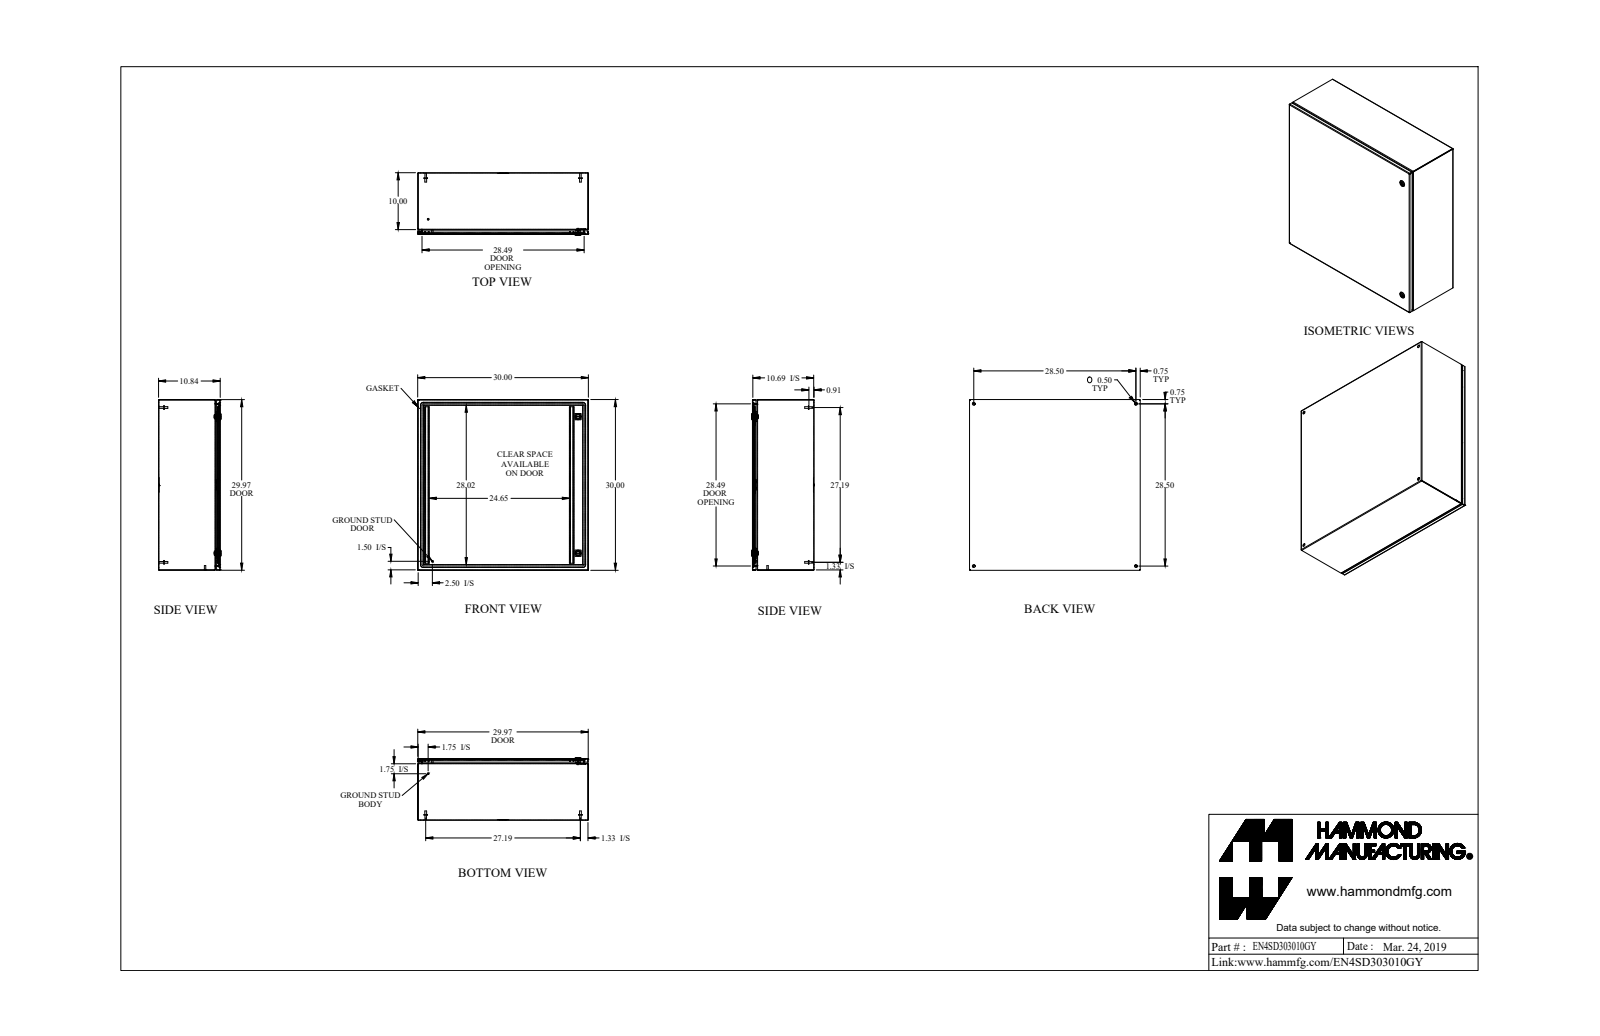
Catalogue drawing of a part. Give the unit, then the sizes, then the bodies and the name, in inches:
Units: inches
Overall size (bounding box): 30 × 30 × 10.997
Round holes (diameter × count): ⌀0.5 ×4, ⌀0.232 ×2, ⌀0.625 ×2, ⌀0.785 ×2, ⌀0.172 ×1, ⌀0.24 ×1, ⌀0.242 ×1
Round bosses / shafts (diameter × count): ⌀0.625 ×4, ⌀0.313 ×4, ⌀0.27 ×4, ⌀1.1 ×2, ⌀0.525 ×2, ⌀0.281 ×2, ⌀0.25 ×2, ⌀0.455 ×1
Partial cylindrical surfaces — rounded edges, fillets, slot ends (radius × count): R0.108 ×24, R0.036 ×16, R0.043 ×12, R0.081 ×12, R0.382 ×12, R19.003 ×8, R0.006 ×6, R0.062 ×6
Main face-to-face distances: 0.072, 10.765, 29.928, 10.693, 10.837, 29.856, 30, 0.837, 9.928, 0.75
Hole centre spacings: 28.5, 2.493, 26.272, 27.519, 37.964, 40.305, 23.999
Volume: 248.1 in³ · Surface area: 6 948 in²
Bodies: 31 solids, 853 faces (395 planar, 294 cylindrical, 164 other)
Part name (STEP PRODUCT): EN4SD303010GY
STEP written by: SolidWorks 2019 (AUTOMOTIVE_DESIGN)
